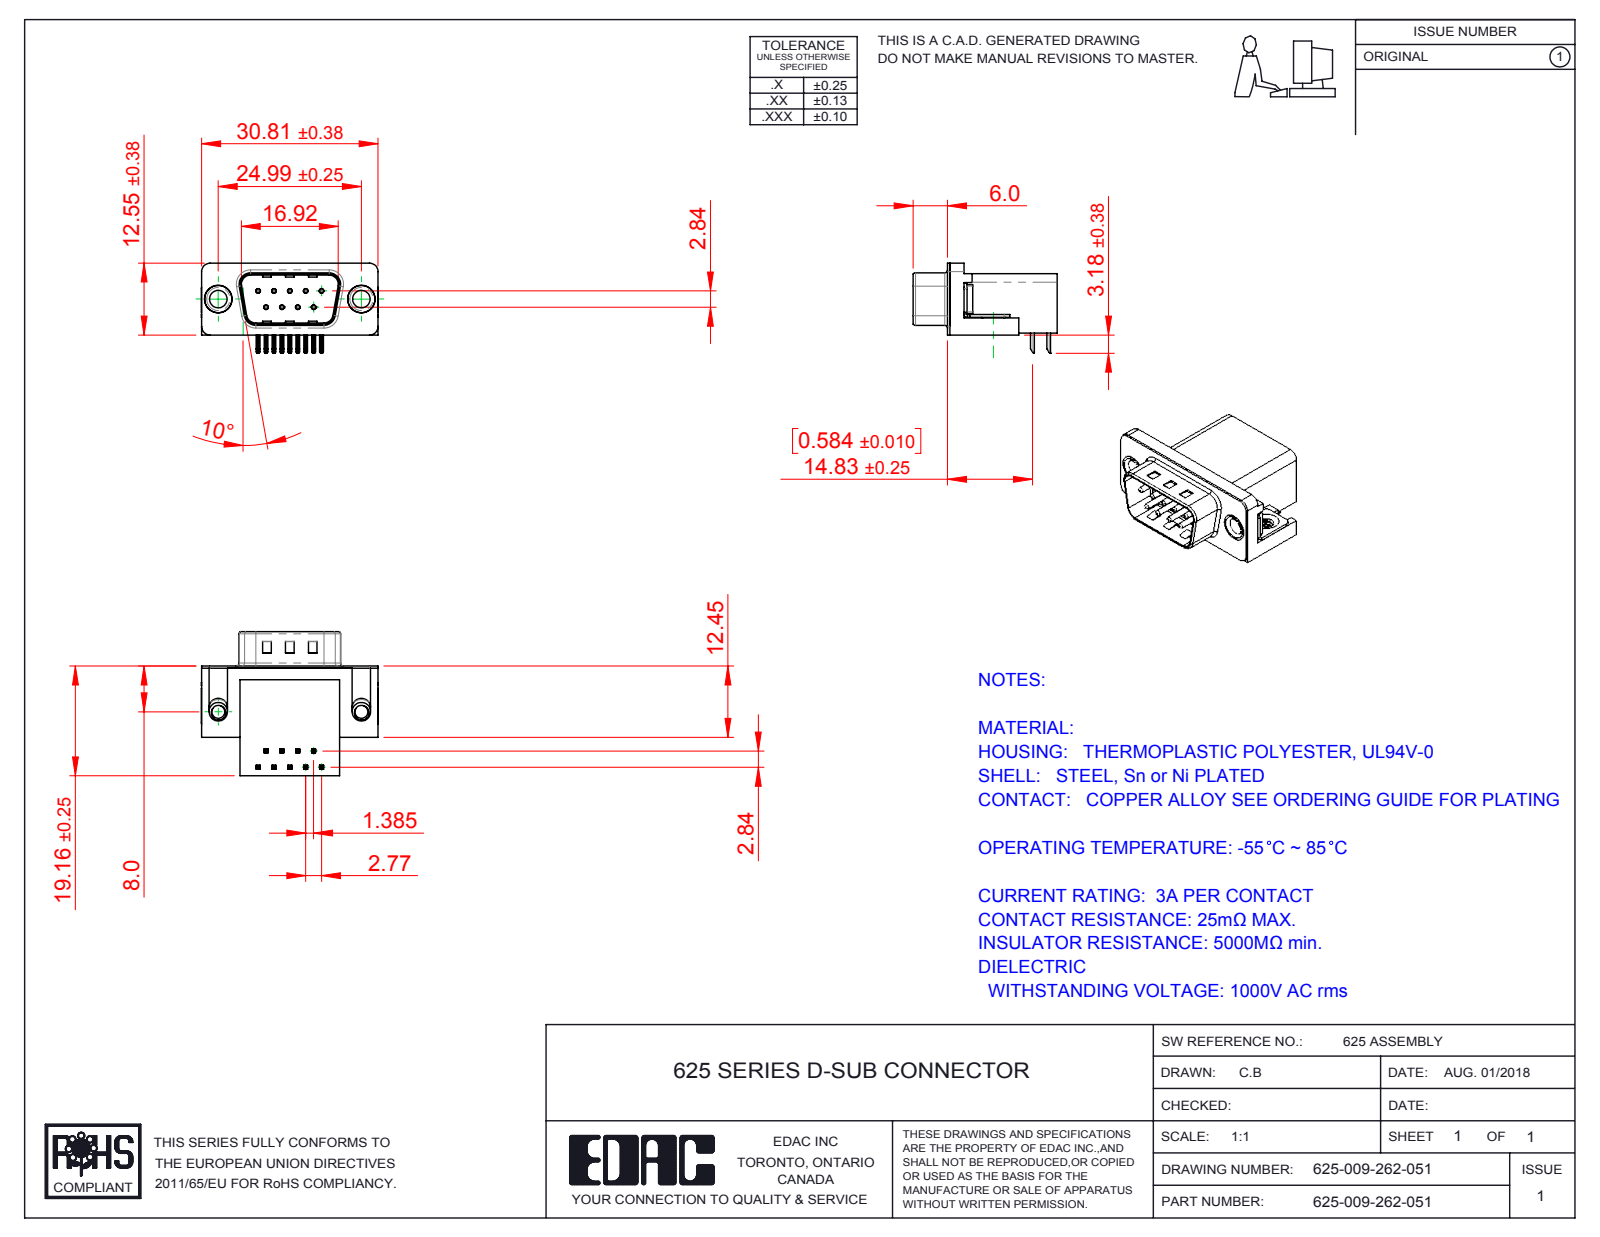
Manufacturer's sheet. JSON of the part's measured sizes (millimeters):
{"part_name": "625 Thru Hole Rivet; 625 Housing_9 Socket; 625 Shell_9 Socket; 625 Contact Bottom (+3 more)", "step_written_by": "SolidWorks 2016 (CONFIG_CONTROL_DESIGN)", "units": "millimeters", "bodies": {"solids": 15, "faces": 985, "planar": 575, "cylindrical": 311, "other": 99}, "overall_size": [30.89, 25.16, 15.73], "volume_mm3": 4474, "surface_area_mm2": 5007, "round_holes": [[0.35, 9], [0.8, 9], [2.26, 2], [3.05, 2], [4, 2], [4.8, 2], [5, 2]], "round_bosses_or_shafts": [[0.75, 9], [4.9, 2], [4.75, 2], [3.85, 2], [3.26, 2]], "partial_cylinders_radius": [[0.25, 44], [0.12, 18], [1, 16], [0.5, 9], [1.5, 8], [1.6, 8], [0.9, 4], [2, 4]], "face_to_face_distances": [0.4, 10.34, 18.76, 19.16, 2.9, 16.26, 2.5, 0.35, 10.69, 6.7], "hole_center_spacings": [3.16, 2.77, 5.54, 5.03, 5.04, 8.31, 7.48, 7.49]}
